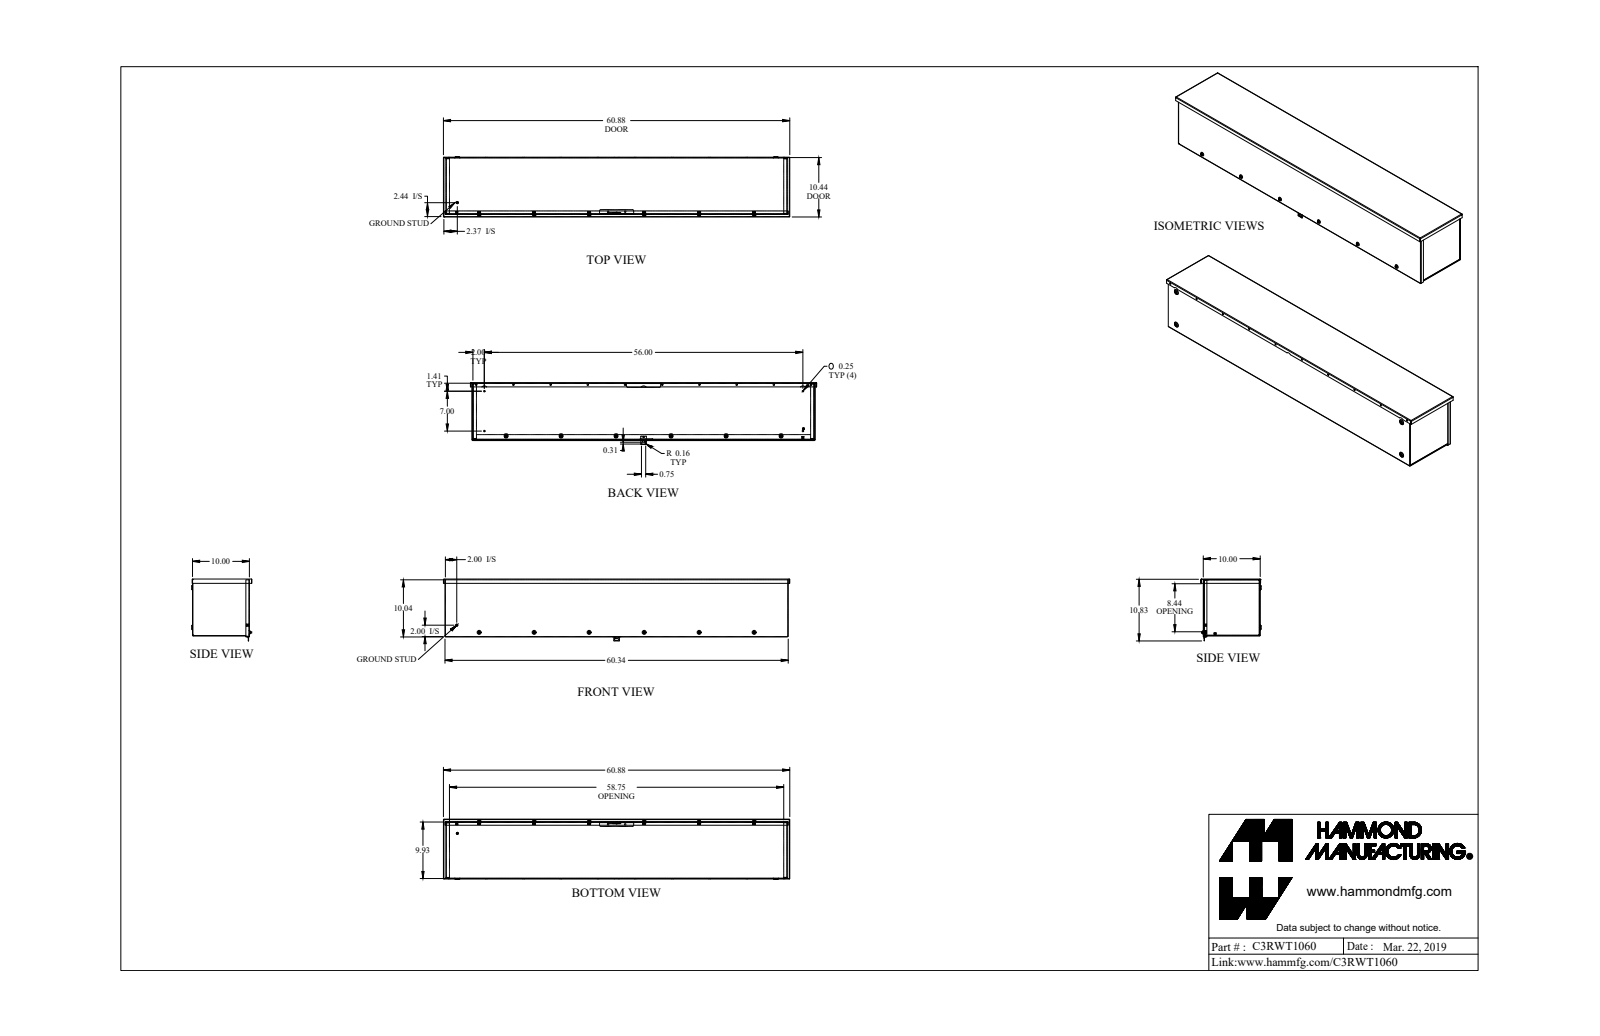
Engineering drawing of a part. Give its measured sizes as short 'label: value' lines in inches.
name: C3RWT1060_Default
written by: SolidWorks 2019 (CONFIG_CONTROL_DESIGN)
unit: in
bodies: 32 solids, 1166 faces (637 planar, 377 cylindrical, 152 other)
size: 60.875 × 10.871 × 10.594
volume: 206 in³; area: 5 775 in²
holes: 16× ⌀0.25, 8× ⌀0.156, 6× ⌀0.214, 6× ⌀0.23, 2× ⌀0.203, 1× ⌀0.125, 1× ⌀0.137, 1× ⌀0.2, 1× ⌀0.215
bosses: 7× ⌀0.19, 6× ⌀0.148, 2× ⌀0.375, 1× ⌀0.5, 1× ⌀0.367, 1× ⌀0.21, 1× ⌀0.152, 1× ⌀0.125
rounds: 24× R0.08, 24× R0.108, 18× R0.036, 18× R0.108, 14× R0.125, 12× R0.022, 6× R0.171, 6× R0.206
face distances: 0.072, 9.928, 10, 9.856, 0.072, 9.856, 9.928, 59.928, 0.144, 60
hole spacings: 6.542, 9.669, 13.083, 13.083, 19.625, 26.167, 32.708, 39.25
